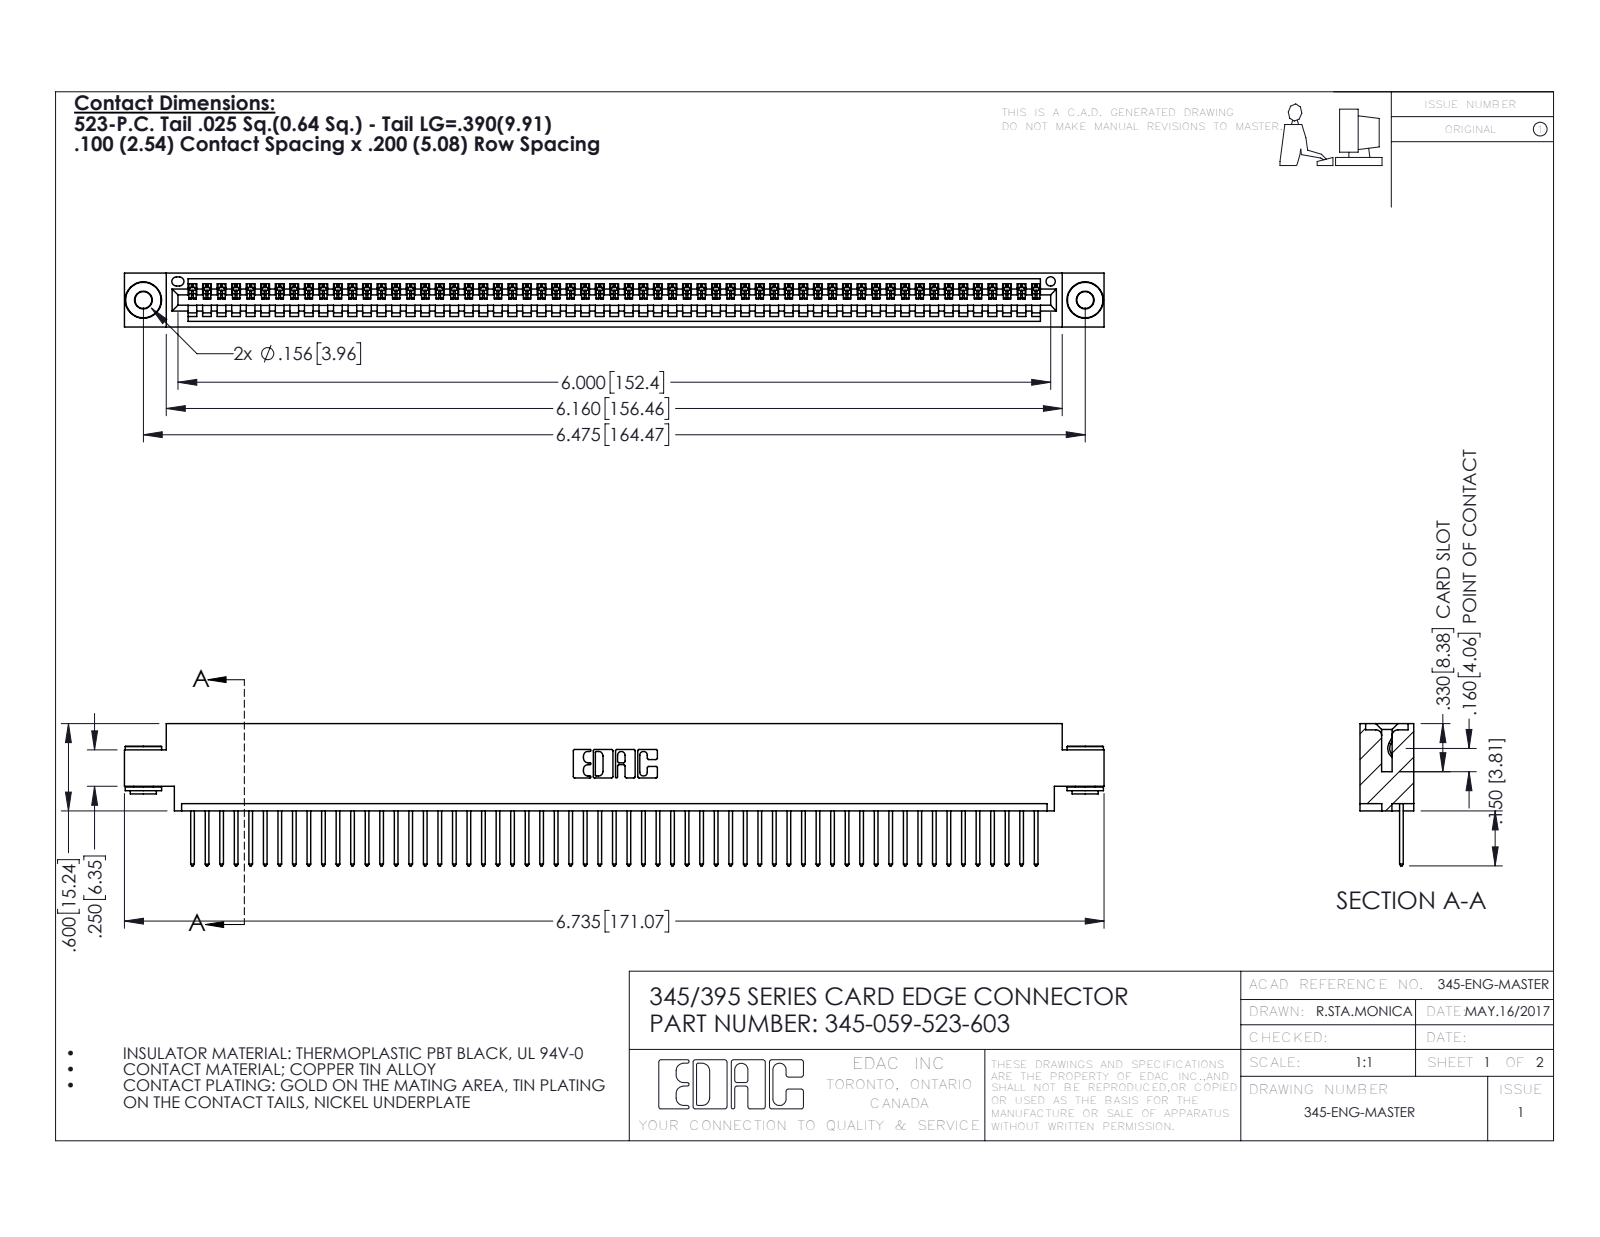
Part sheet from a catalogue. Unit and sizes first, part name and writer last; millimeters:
Units: millimetres
Overall size (bounding box): 171.1 × 24.8 × 9.4
Round holes (diameter × count): ⌀2.9 ×2, ⌀4 ×2, ⌀1.6 ×1
Round bosses / shafts (diameter × count): ⌀6.4 ×2, ⌀4.6 ×2, ⌀3.5 ×2
Partial cylindrical surfaces — rounded edges, fillets, slot ends (radius × count): R0.2 ×118, R0.3 ×118, R0.3 ×22, R0.2 ×6, R0.8 ×6, R0.7 ×3, R0.8 ×2, R1 ×2
Main face-to-face distances: 1.8, 7.6, 9.4, 2.5, 6.9, 0.6, 5.1, 5.7, 4.4, 3.8
Hole centre spacings: 6.9, 158.5, 164.5
Volume: 16 300 mm³ · Surface area: 22 260 mm²
Bodies: 62 solids, 3590 faces (2454 planar, 1128 cylindrical, 8 other)
Part name (STEP PRODUCT): 345 Part_0.170 Offset - 0.156 Dia-TH; 345-292-001_345-293-123; 345-250-002_345-250-002-102; 345-059-523-603
STEP written by: SolidWorks 2016 (CONFIG_CONTROL_DESIGN)
